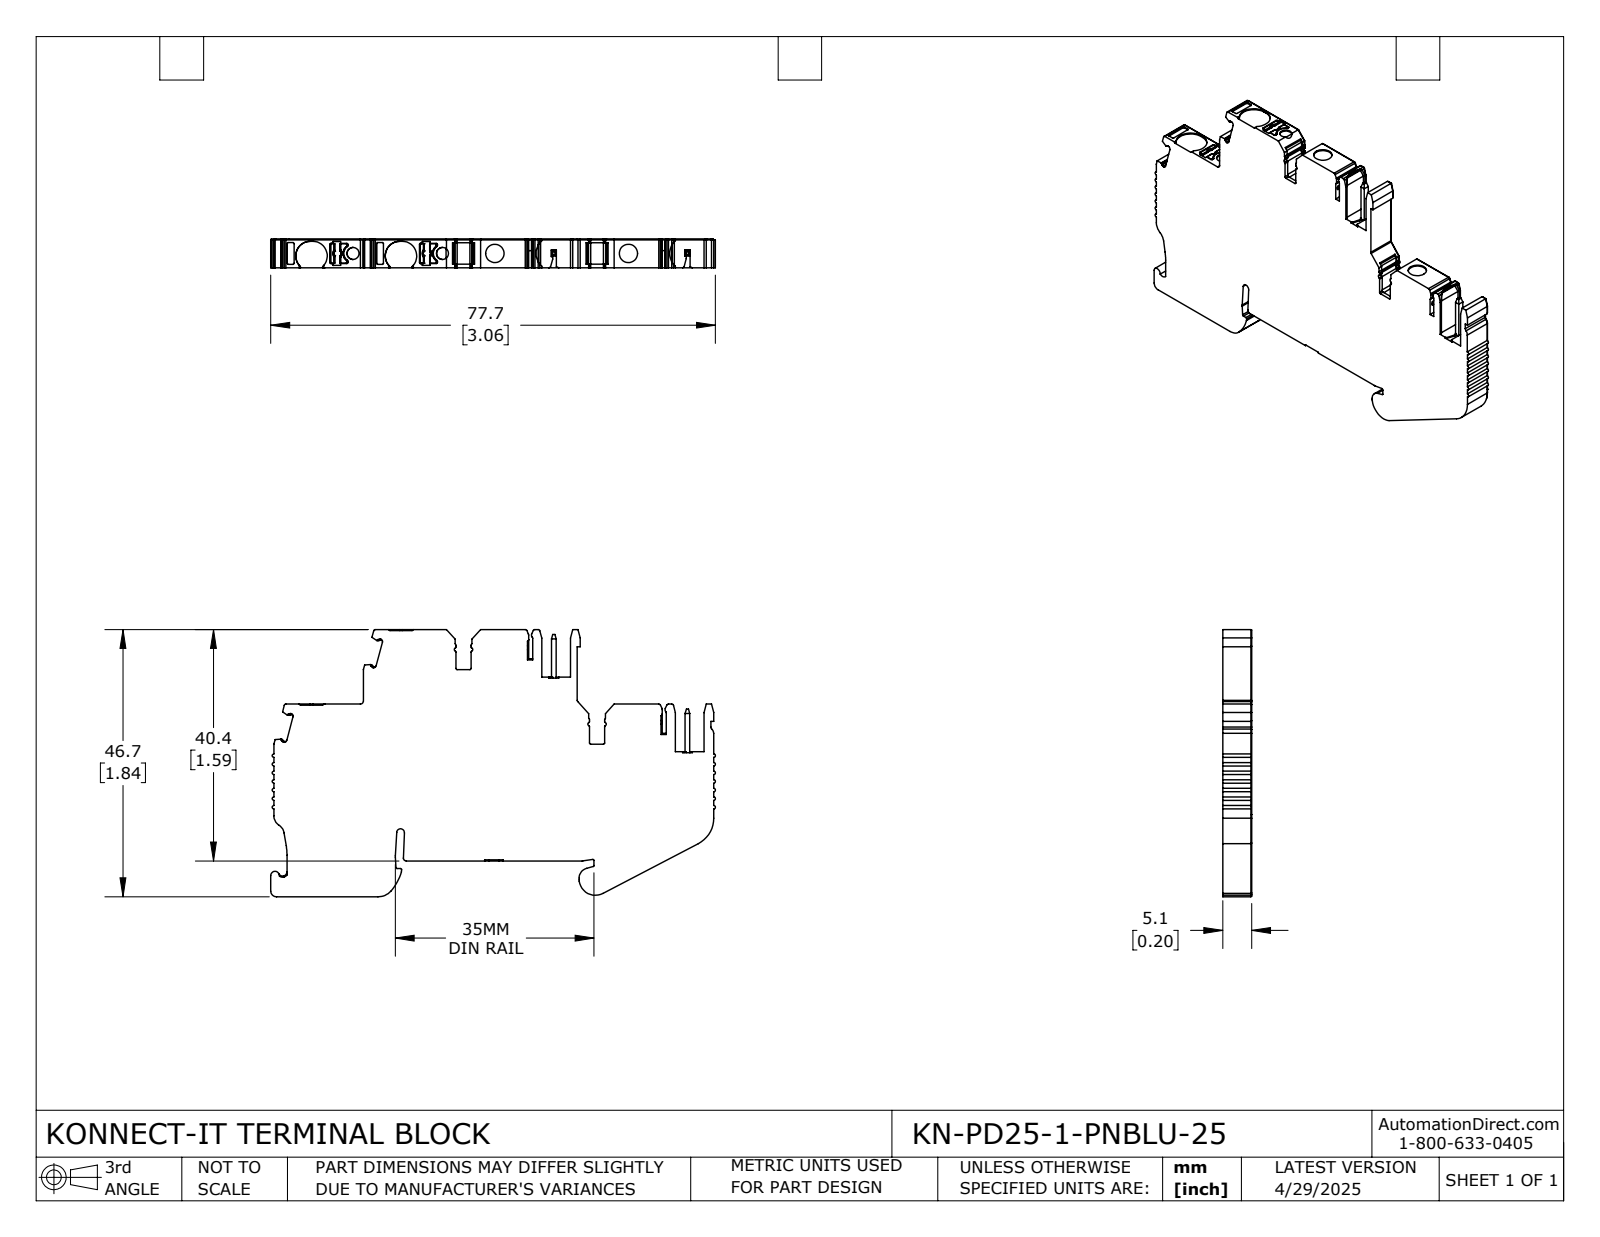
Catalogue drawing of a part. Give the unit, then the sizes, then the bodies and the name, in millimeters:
Units: millimetres
Overall size (bounding box): 77.65 × 46.65 × 5.05
Round holes (diameter × count): ⌀2.1 ×2, ⌀3.2 ×2
Partial cylindrical surfaces — rounded edges, fillets, slot ends (radius × count): R0.2 ×58, R0.3 ×48, R0.1 ×23, R0.4 ×16, R0.5 ×16, R0.15 ×8, R0.6 ×6, R0.16 ×4
Main face-to-face distances: 5.05, 13.02, 23.33, 6.25, 33.63, 27.38, 46.65, 40.4, 5.2, 27.18
Hole centre spacings: 9.14, 15.62, 23.33, 24.76, 32.47, 48.09
Volume: 12 886 mm³ · Surface area: 7 022 mm²
Bodies: 1 solid, 727 faces (387 planar, 302 cylindrical, 38 other)
Part name (STEP PRODUCT): KN-PD25-1-PNBLU-25
STEP written by: SolidWorks 2024 (CONFIG_CONTROL_DESIGN)
